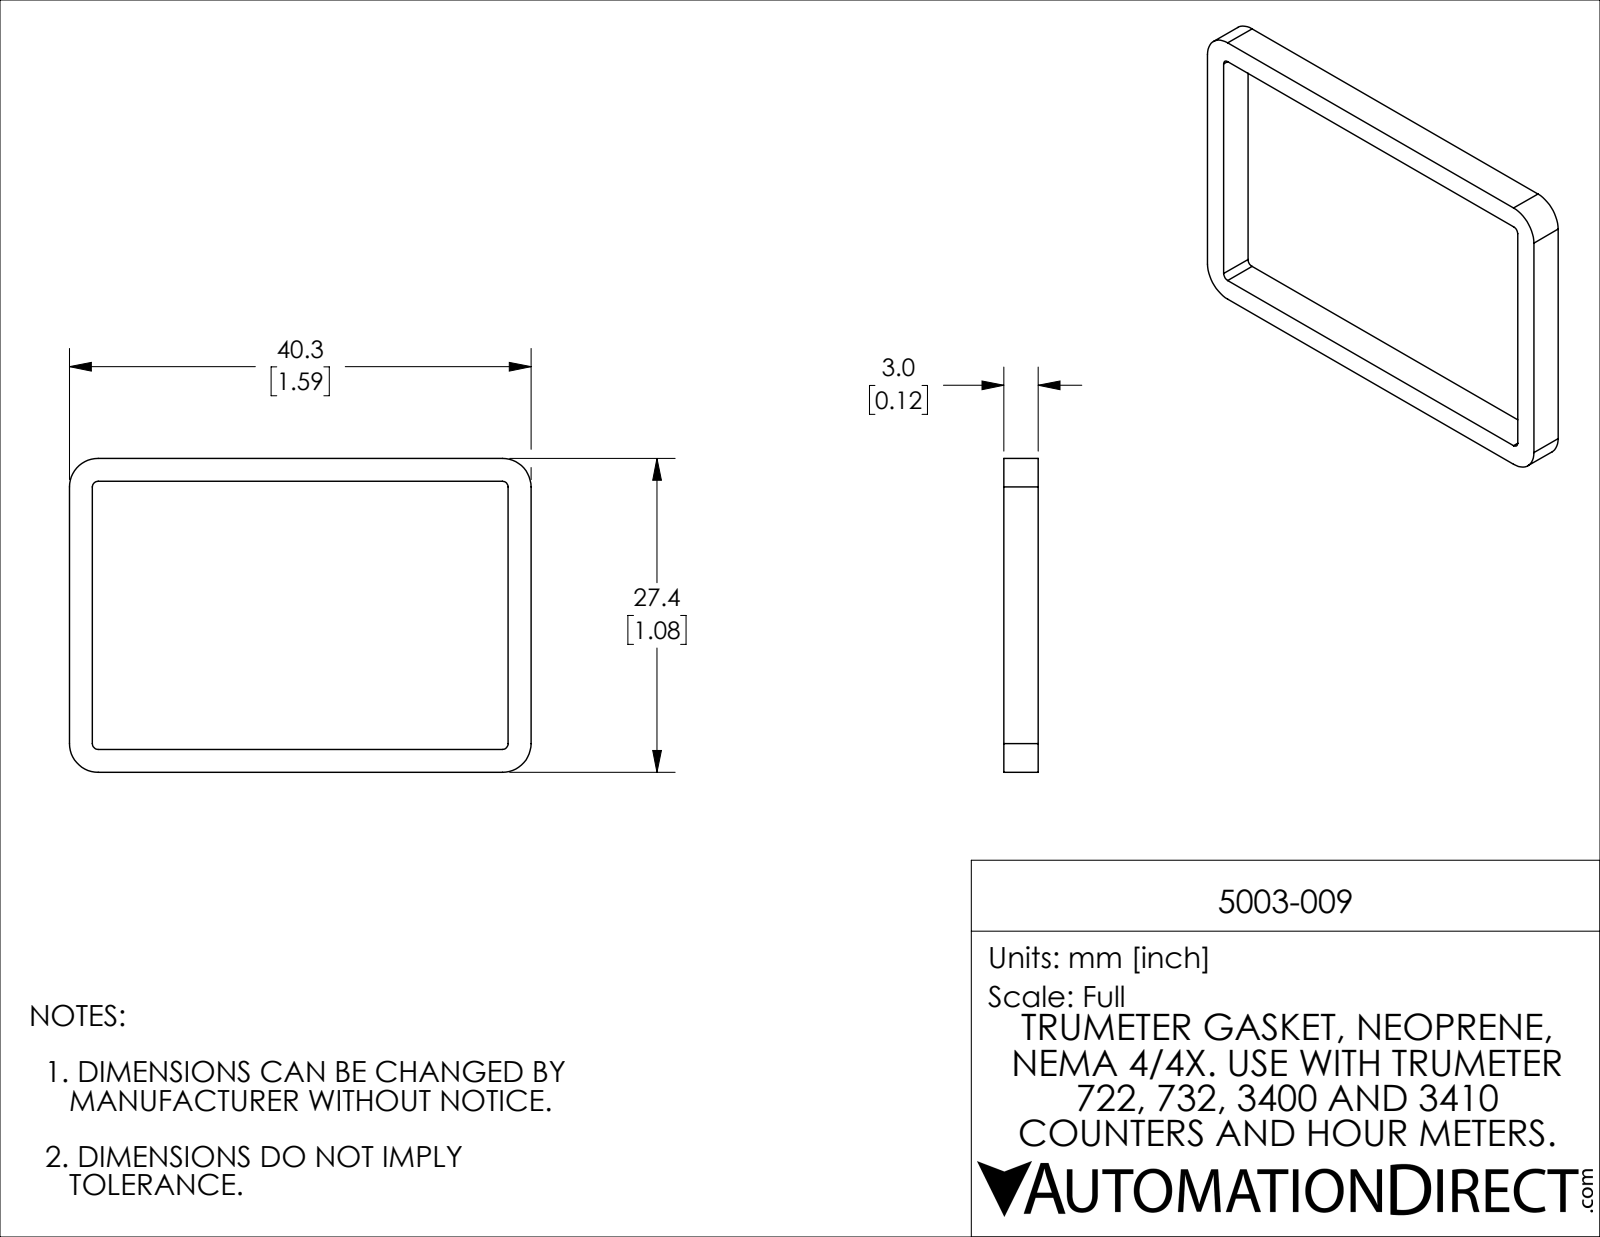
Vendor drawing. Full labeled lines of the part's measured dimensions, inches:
Part name (STEP PRODUCT): 5003-009
STEP written by: SolidWorks 2021 (CONFIG_CONTROL_DESIGN)
Units: inches
Bodies: 1 solid, 18 faces (10 planar, 8 cylindrical, 0 other)
Overall size (bounding box): 1.587 × 1.079 × 0.118
Volume: 0.046 in³ · Surface area: 1.935 in²
Partial cylindrical surfaces — rounded edges, fillets, slot ends (radius × count): R0.02 ×4, R0.098 ×4
Main face-to-face distances: 0.079, 0.118, 1, 1.508, 1.079, 0.921, 1.429, 1.587
